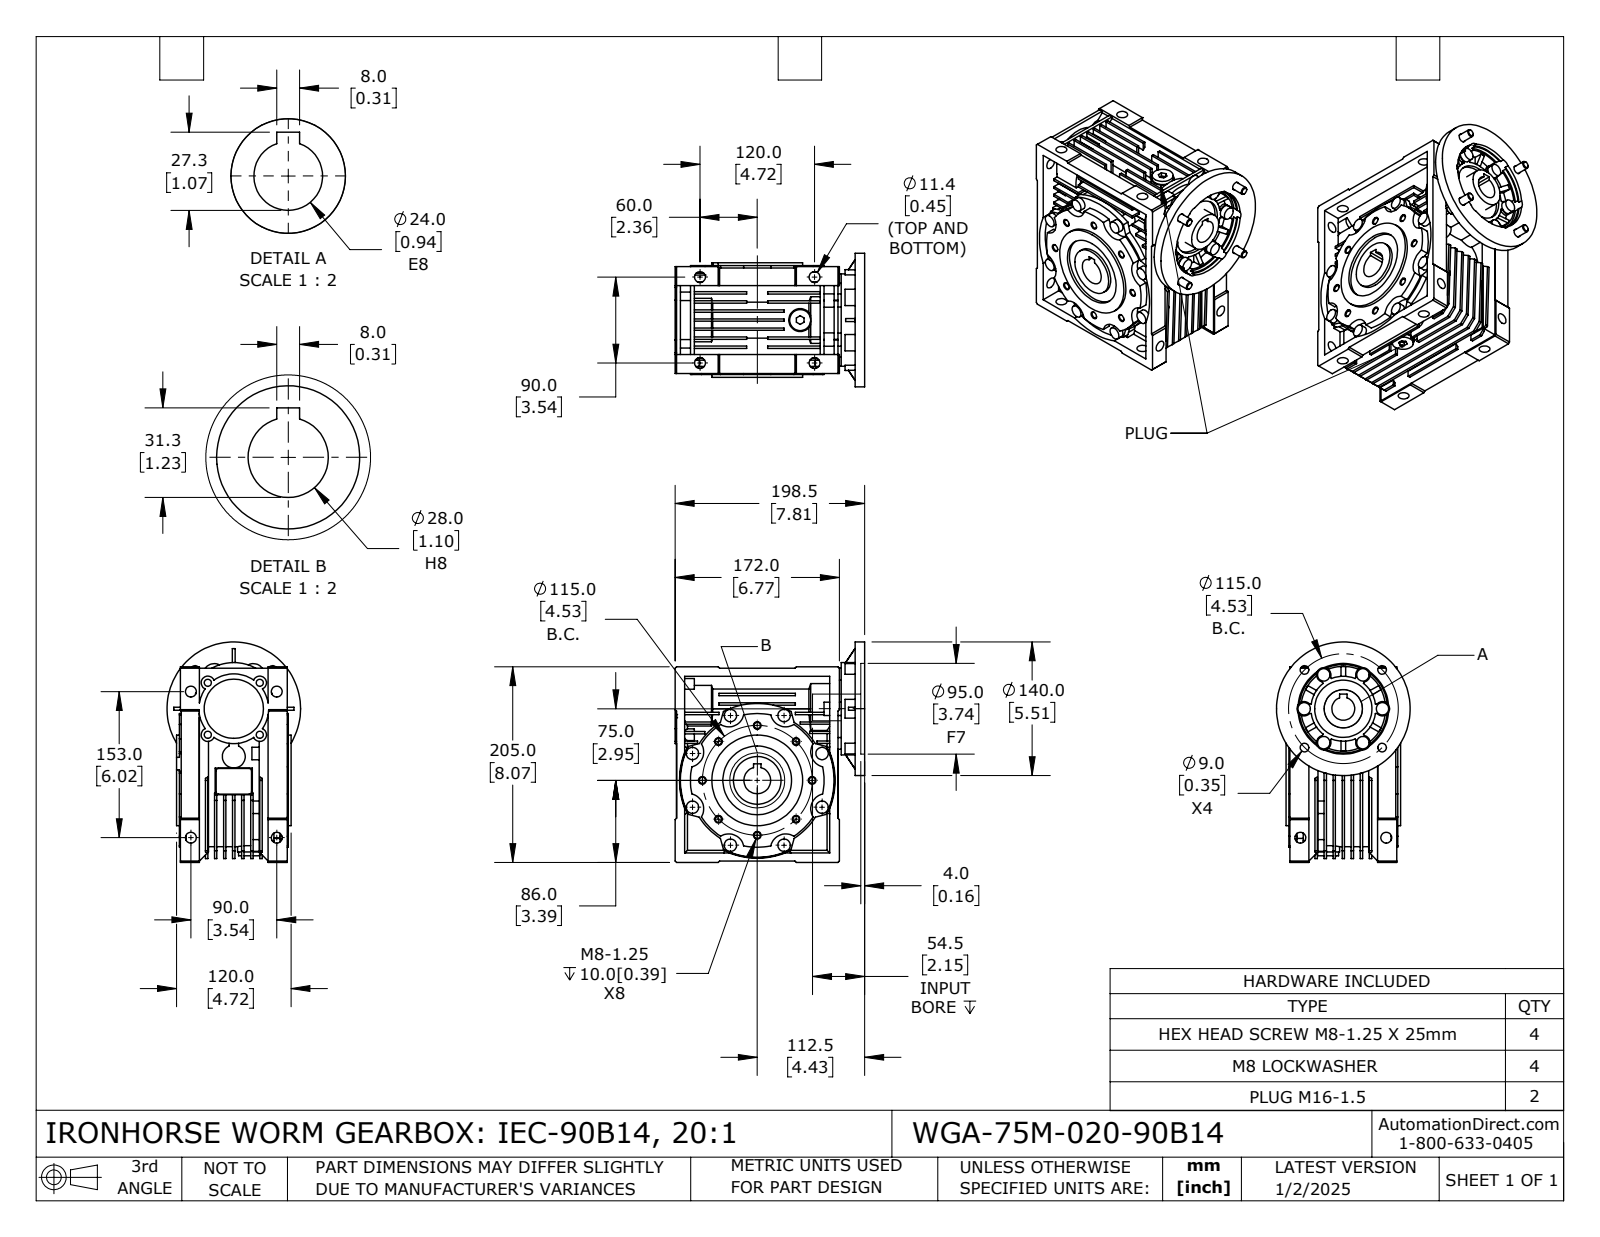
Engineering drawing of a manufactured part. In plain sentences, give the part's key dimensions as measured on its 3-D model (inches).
The part is named "WGA-75M-020-90B14". Its 3-D file was written by "SolidWorks 2024 (CONFIG_CONTROL_DESIGN)". It is 16 solids with 1349 faces: 749 planar, 444 cylindrical and 156 other. Overall it measures 9.094 by 8.327 by 5.512 inches. Its volume is 176.2 cubic inches and its surface area 769.9 square inches. Round holes: 8 of diameter 0.262, 8 of diameter 0.448, 4 of diameter 0.293, 4 of diameter 0.323, 4 of diameter 0.354, 2 of diameter 0.571, 1 of diameter 0.945, 1 of diameter 0.984, 1 of diameter 1.102, 1 of diameter 1.535, 1 of diameter 1.654, 1 of diameter 1.969. Round bosses or shafts: 14 of diameter 0.512, 4 of diameter 0.606, 4 of diameter 0.315, 3 of diameter 0.945, 2 of diameter 0.866, 2 of diameter 0.622, 2 of diameter 0.539, 1 of diameter 5.512. Partial cylindrical surfaces (rounded edges, fillets, slot ends): 10 of radius 0.276, 8 of radius 0.63, 6 of radius 0.295, 6 of radius 0.463, 4 of radius 0.098, 1 of radius 1.417, 1 of radius 1.437, 1 of radius 1.535. The main face-to-face distances are 0.374, 0.098, 0.748, 0.472, 0.394, 0.276, 1.122, 0.65, 1.093, 0.846. The hole center spacings are 2.264, 3.202, 1.733, 2.724, 4.183, 4.528, 0.748, 1.515.
